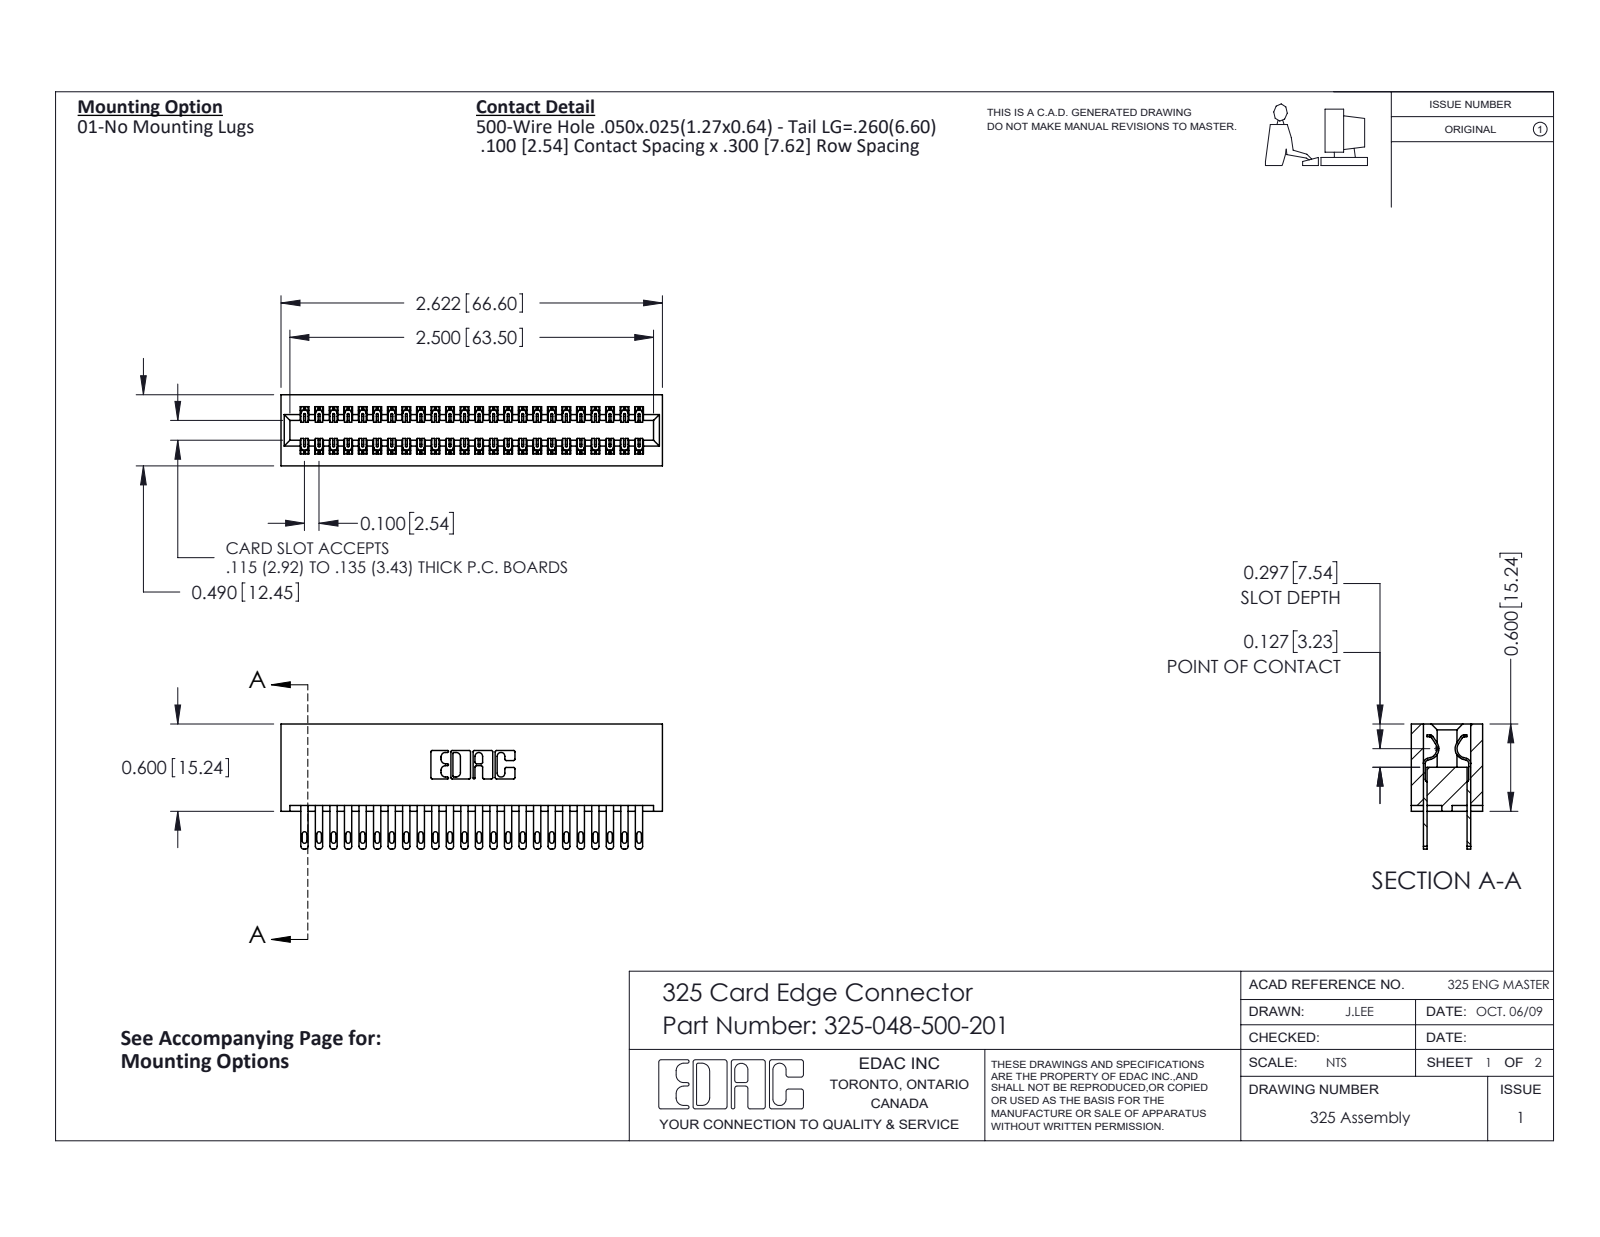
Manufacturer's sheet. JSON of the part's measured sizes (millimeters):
{"part_name": "325 Part_Lugless; 325-292-001_325-293-100; 325-048-500-201", "step_written_by": "SolidWorks 2016 (CONFIG_CONTROL_DESIGN)", "units": "millimeters", "bodies": {"solids": 49, "faces": 2410, "planar": 1506, "cylindrical": 904, "other": 0}, "overall_size": [66.6, 21.8, 12.4], "volume_mm3": 9190, "surface_area_mm2": 11860, "partial_cylinders_radius": [[0.2, 72], [0.4, 48], [0.5, 48], [0.3, 22], [0.2, 6], [0.8, 6], [0.7, 3], [0.4, 2]], "face_to_face_distances": [2.1, 10.3, 7.6, 2.7, 9.7, 0.6, 8.3, 12.4, 7, 14.2]}
